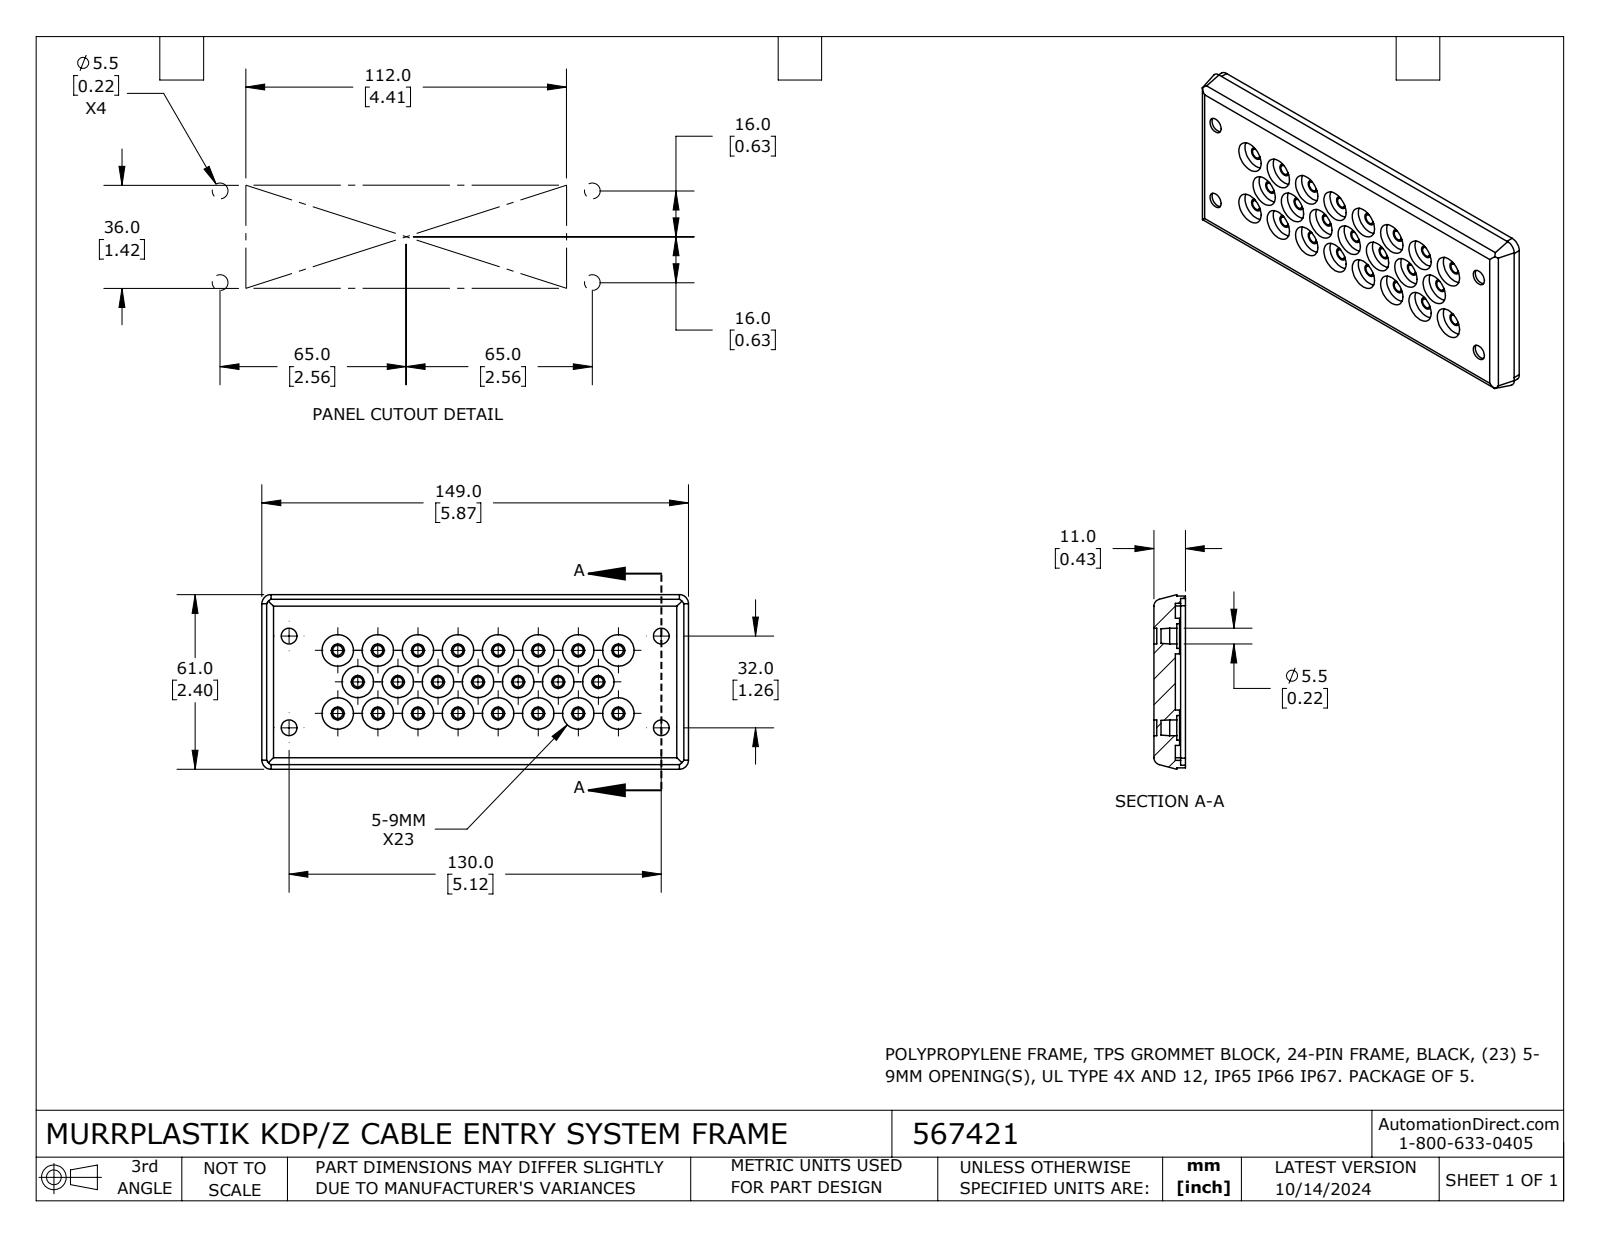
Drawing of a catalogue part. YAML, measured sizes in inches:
part_name: "567421"
step_written_by: "SolidWorks 2023 (CONFIG_CONTROL_DESIGN)"
units: inches
bodies: {solids: 1, faces: 340, planar: 120, cylindrical: 208, other: 12}
overall_size: [5.866, 2.402, 0.433]
volume: 2.913
surface_area: 46.05
round_holes:
  - {diameter: 0.177, count: 23}
  - {diameter: 0.432, count: 12}
  - {diameter: 0.432, count: 11}
  - {diameter: 0.217, count: 4}
  - {diameter: 0.339, count: 4}
round_bosses_or_shafts:
  - {diameter: 0.138, count: 23}
  - {diameter: 0.488, count: 4}
partial_cylinders:
  - {radius: 0.012, count: 16}
  - {radius: 0.035, count: 4}
  - {radius: 0.098, count: 4}
  - {radius: 0.098, count: 4}
  - {radius: 0.138, count: 4}
  - {radius: 0.305, count: 4}
face_to_face_distances: [0.217, 0.098, 0.118, 0.079, 0.177, 0.295, 0.067, 0.433, 0.347, 2.015]
hole_center_spacings: [0.513, 0.933, 0.551, 1.444, 1.102, 1.977, 1.027, 1.654]
